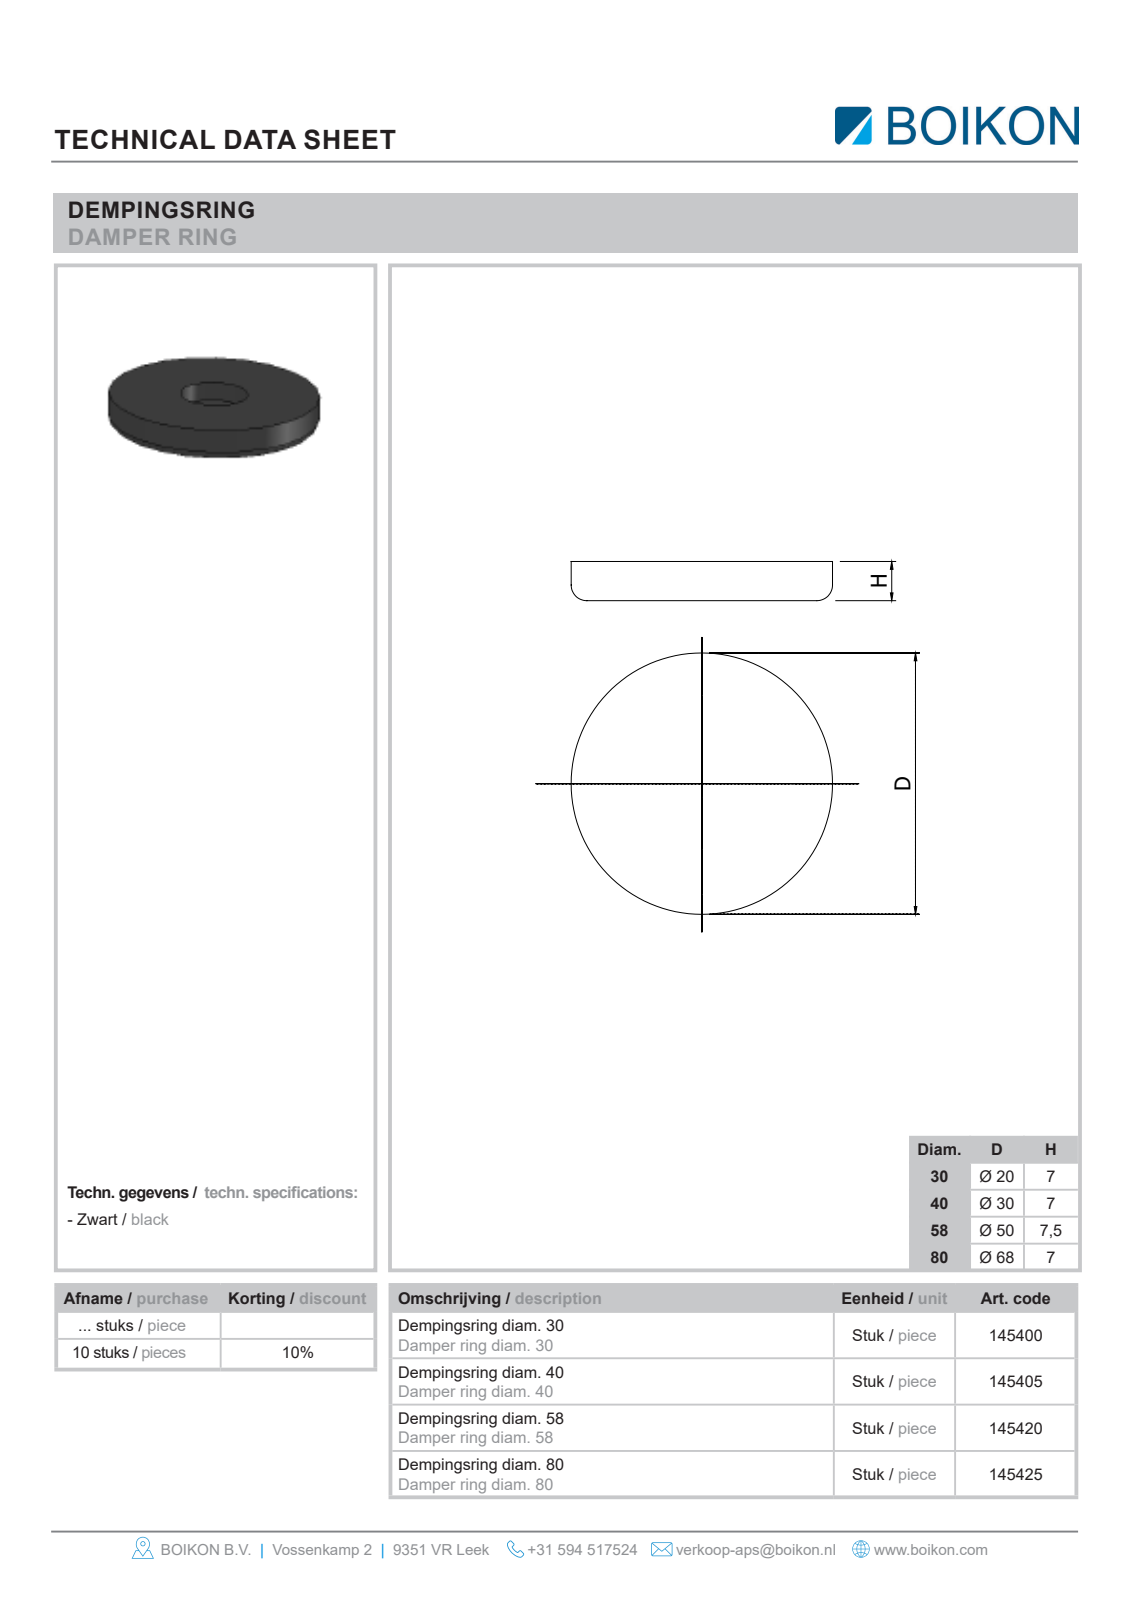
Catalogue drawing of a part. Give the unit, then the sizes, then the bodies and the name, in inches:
Units: inches
Overall size (bounding box): 1.181 × 1.181 × 0.276
Round holes (diameter × count): ⌀0.63 ×1
Round bosses / shafts (diameter × count): ⌀1.181 ×1
Main face-to-face distances: 0.276, 0.098, 0.177
Volume: 0.242 in³ · Surface area: 3.436 in²
Bodies: 1 solid, 6 faces (3 planar, 2 cylindrical, 1 other)
Part name (STEP PRODUCT): Root; 145405Dempingsring diam. 40BOIKON
STEP written by: HiCAD 2013 1802.4 Build 509 (AUTOMOTIVE_DESIGN)
